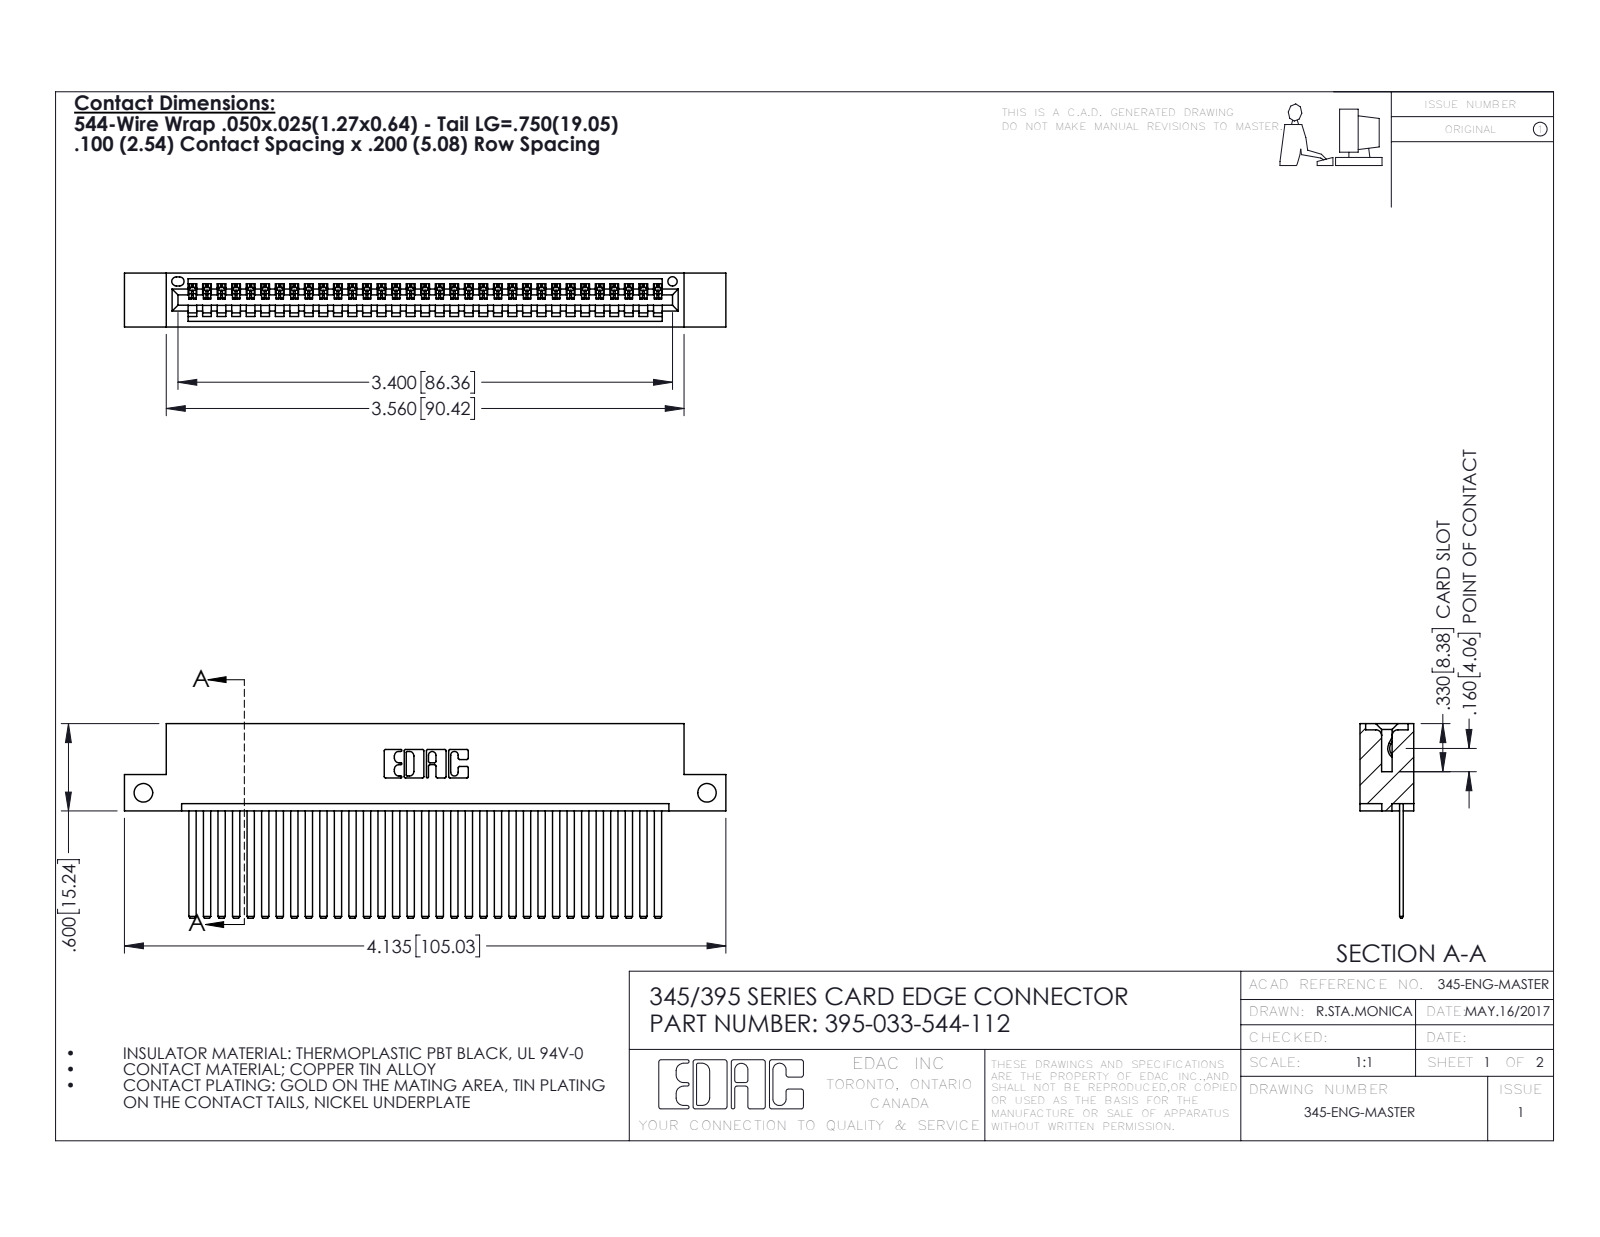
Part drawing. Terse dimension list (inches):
name: 395-033-544-112; 345-292-001_345-293-144; 345 Part_Flush Mounting Lugs - Side Mount
written by: SolidWorks 2016 (CONFIG_CONTROL_DESIGN)
unit: in
bodies: 34 solids, 1842 faces (1268 planar, 574 cylindrical, 0 other)
size: 4.135 × 1.337 × 0.37
volume: 0.622 in³; area: 22.37 in²
holes: 2× ⌀0.128, 1× ⌀0.064
rounds: 66× R0.006, 22× R0.01, 6× R0.007, 6× R0.031, 3× R0.026, 2× R0.031, 2× R0.04, 1× R0.014
face distances: 0.072, 0.298, 0.025, 0.098, 0.272, 0.2, 0.37, 0.225, 0.149, 0.072
hole spacings: 3.875
